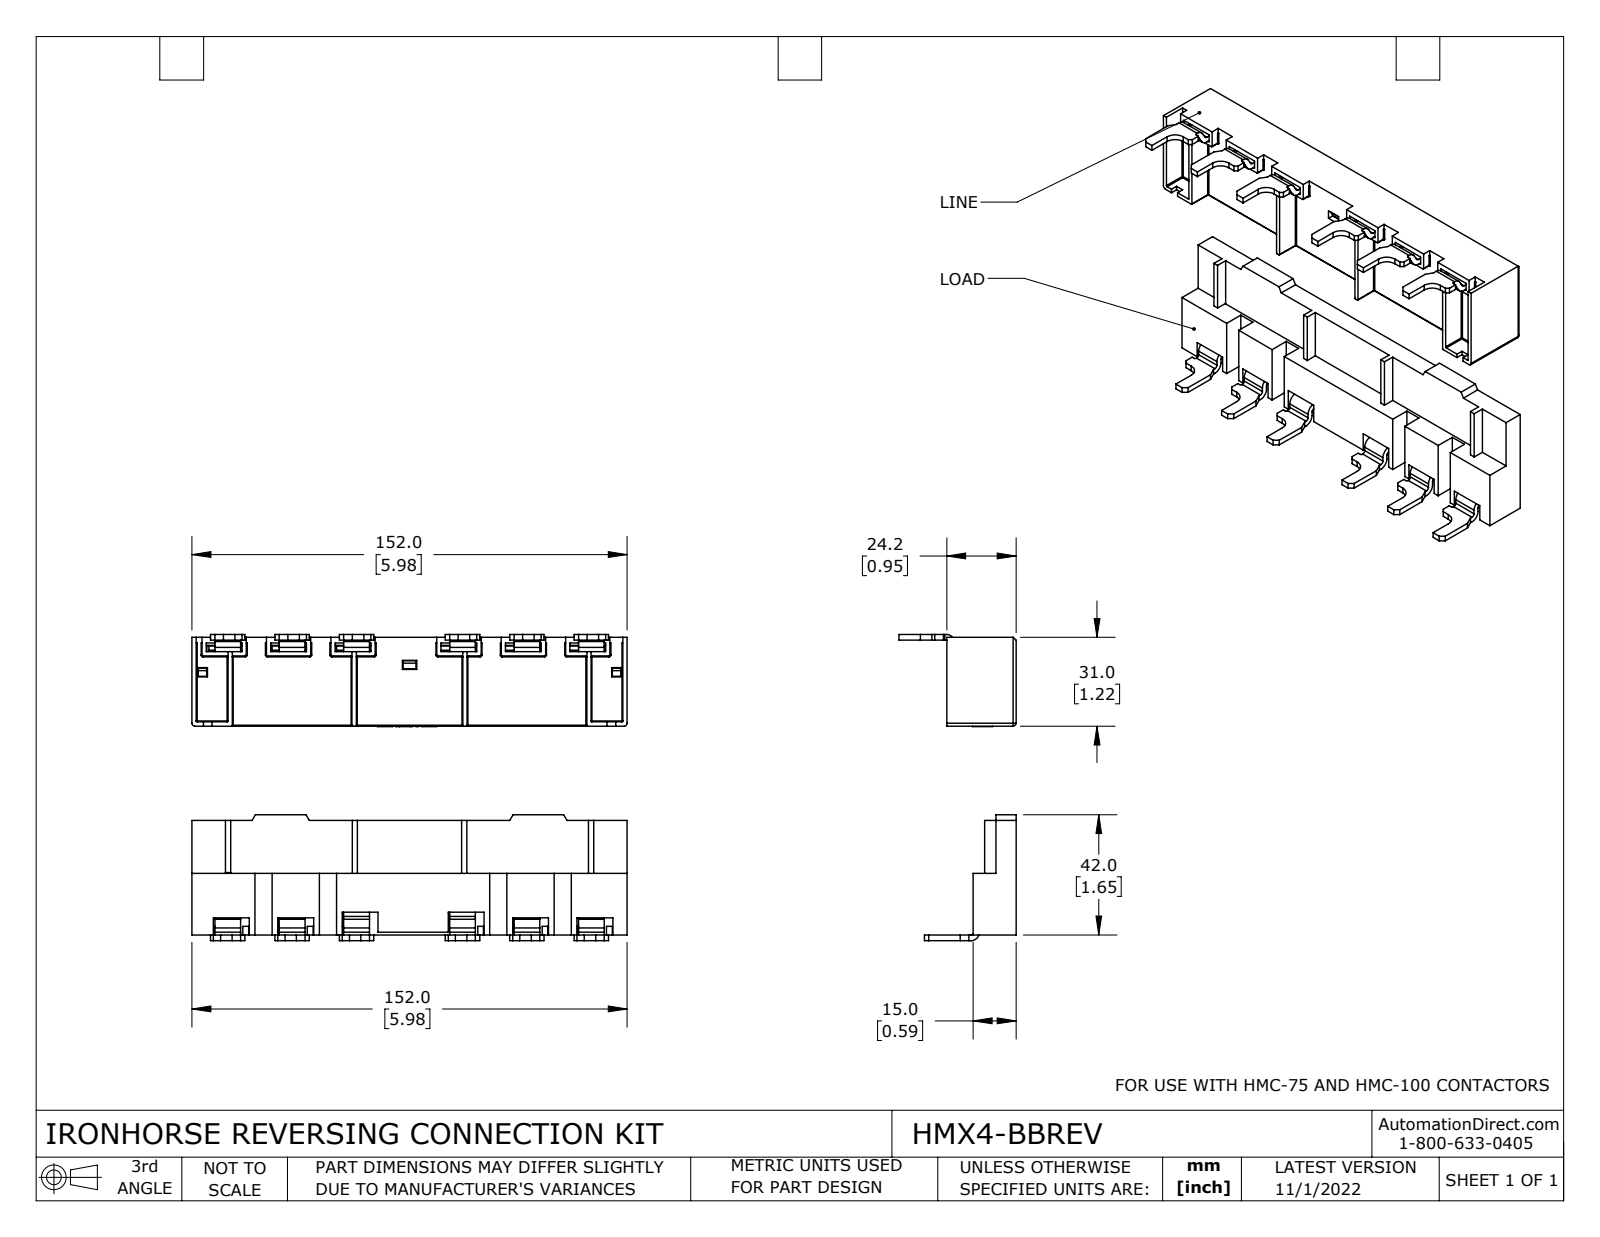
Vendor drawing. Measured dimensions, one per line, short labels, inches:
name: HMX4-BBREV-LINE; HMX4-BBREV; HMX4-BBREV-LOAD
written by: SolidWorks 2021 (CONFIG_CONTROL_DESIGN)
unit: in
bodies: 8 solids, 1006 faces (746 planar, 216 cylindrical, 44 other)
size: 5.984 × 4.209 × 1.61
volume: 7.922 in³; area: 148.3 in²
rounds: 81× R0.012, 18× R0.02, 16× R0.039, 12× R0.157, 8× R0.118, 2× R0.079
face distances: 0.181, 0.091, 0.079, 0.102, 0.362, 0.272, 0.087, 0.189, 0.283, 0.193
